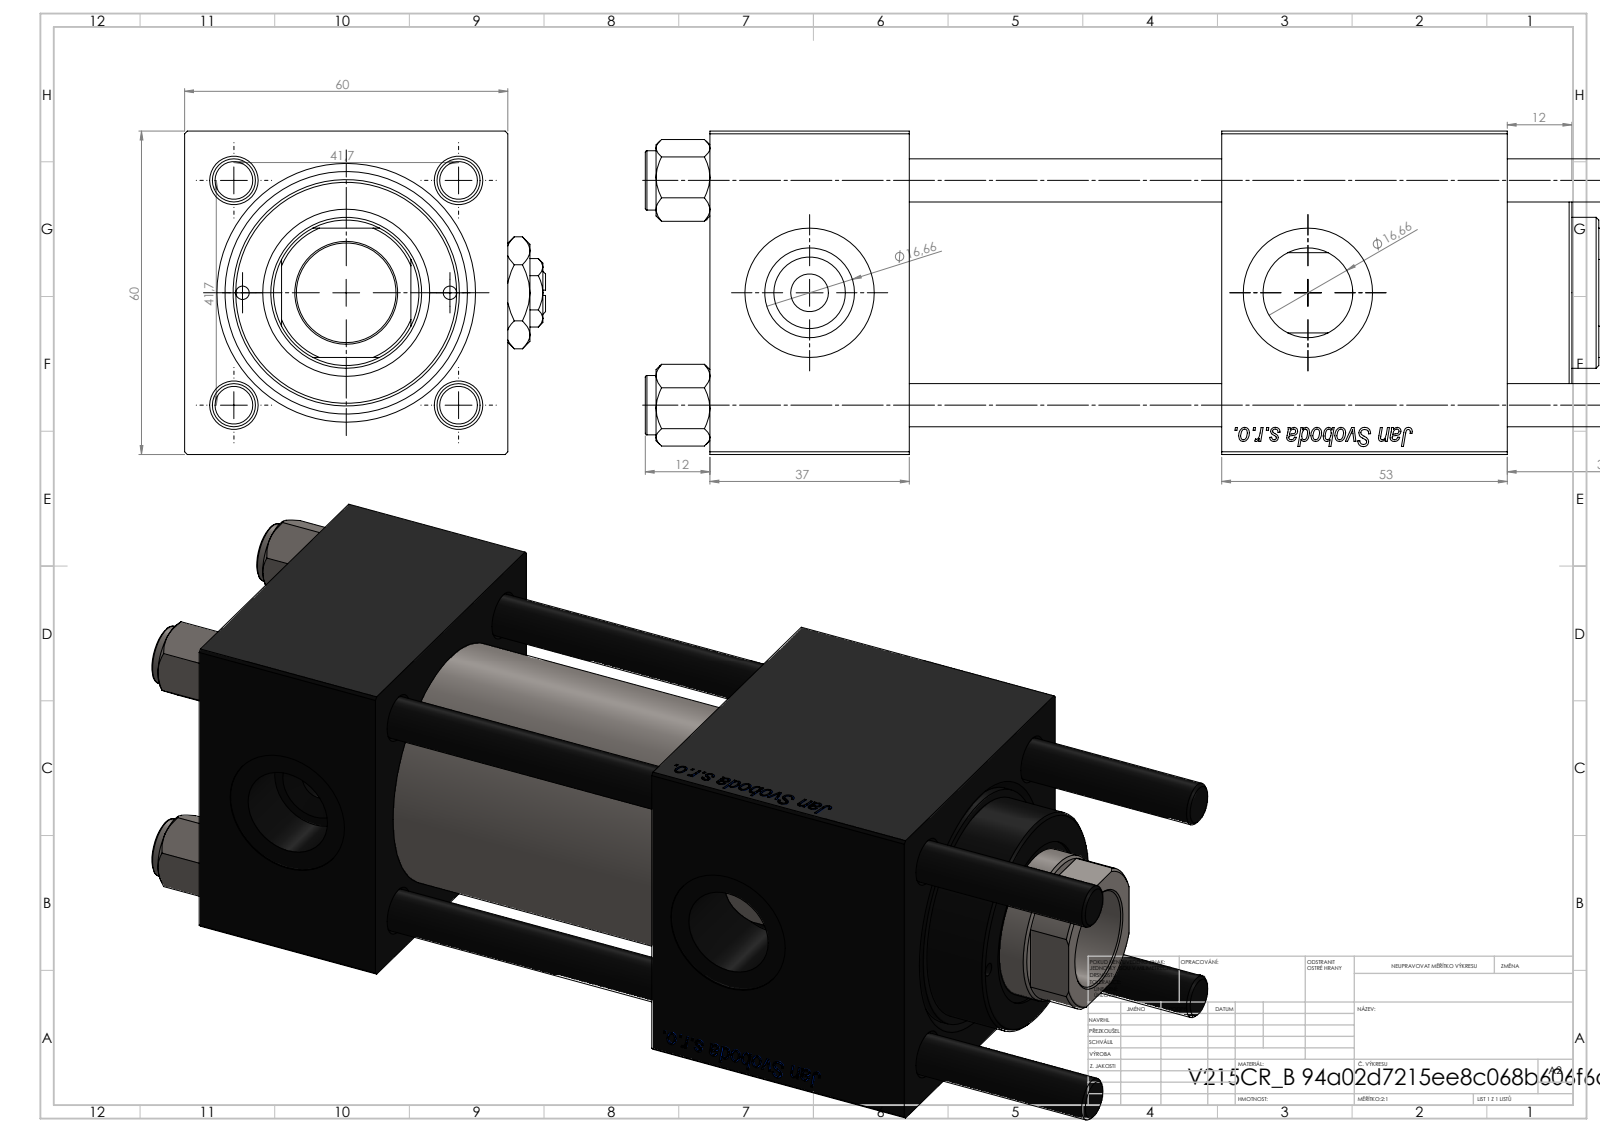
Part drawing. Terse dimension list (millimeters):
name: V215CR_B_TYCINKA; V215_VC_A; V215CR_VCP_B; NUT_M5_B (+2 more)
written by: SolidWorks 2019 (CONFIG_CONTROL_DESIGN)
unit: mm
bodies: 12 solids, 1213 faces (459 planar, 86 cylindrical, 668 other)
size: 195 × 67 × 60
volume: 433 517 mm³; area: 121 390 mm²
holes: 4× ⌀8, 2× ⌀2.5, 2× ⌀7, 2× ⌀16.66, 2× ⌀24, 1× ⌀18.5, 1× ⌀28, 1× ⌀31, 1× ⌀40, 1× ⌀45
bosses: 4× ⌀11, 1× ⌀46, 1× ⌀42
rounds: 1× R13.5
face distances: 60, 37, 58, 95, 53, 119.3, 82.3, 24.3, 148, 111
hole spacings: 20.91, 29.49, 41.7, 45.2, 19.25, 58.97, 38.5, 92.5
